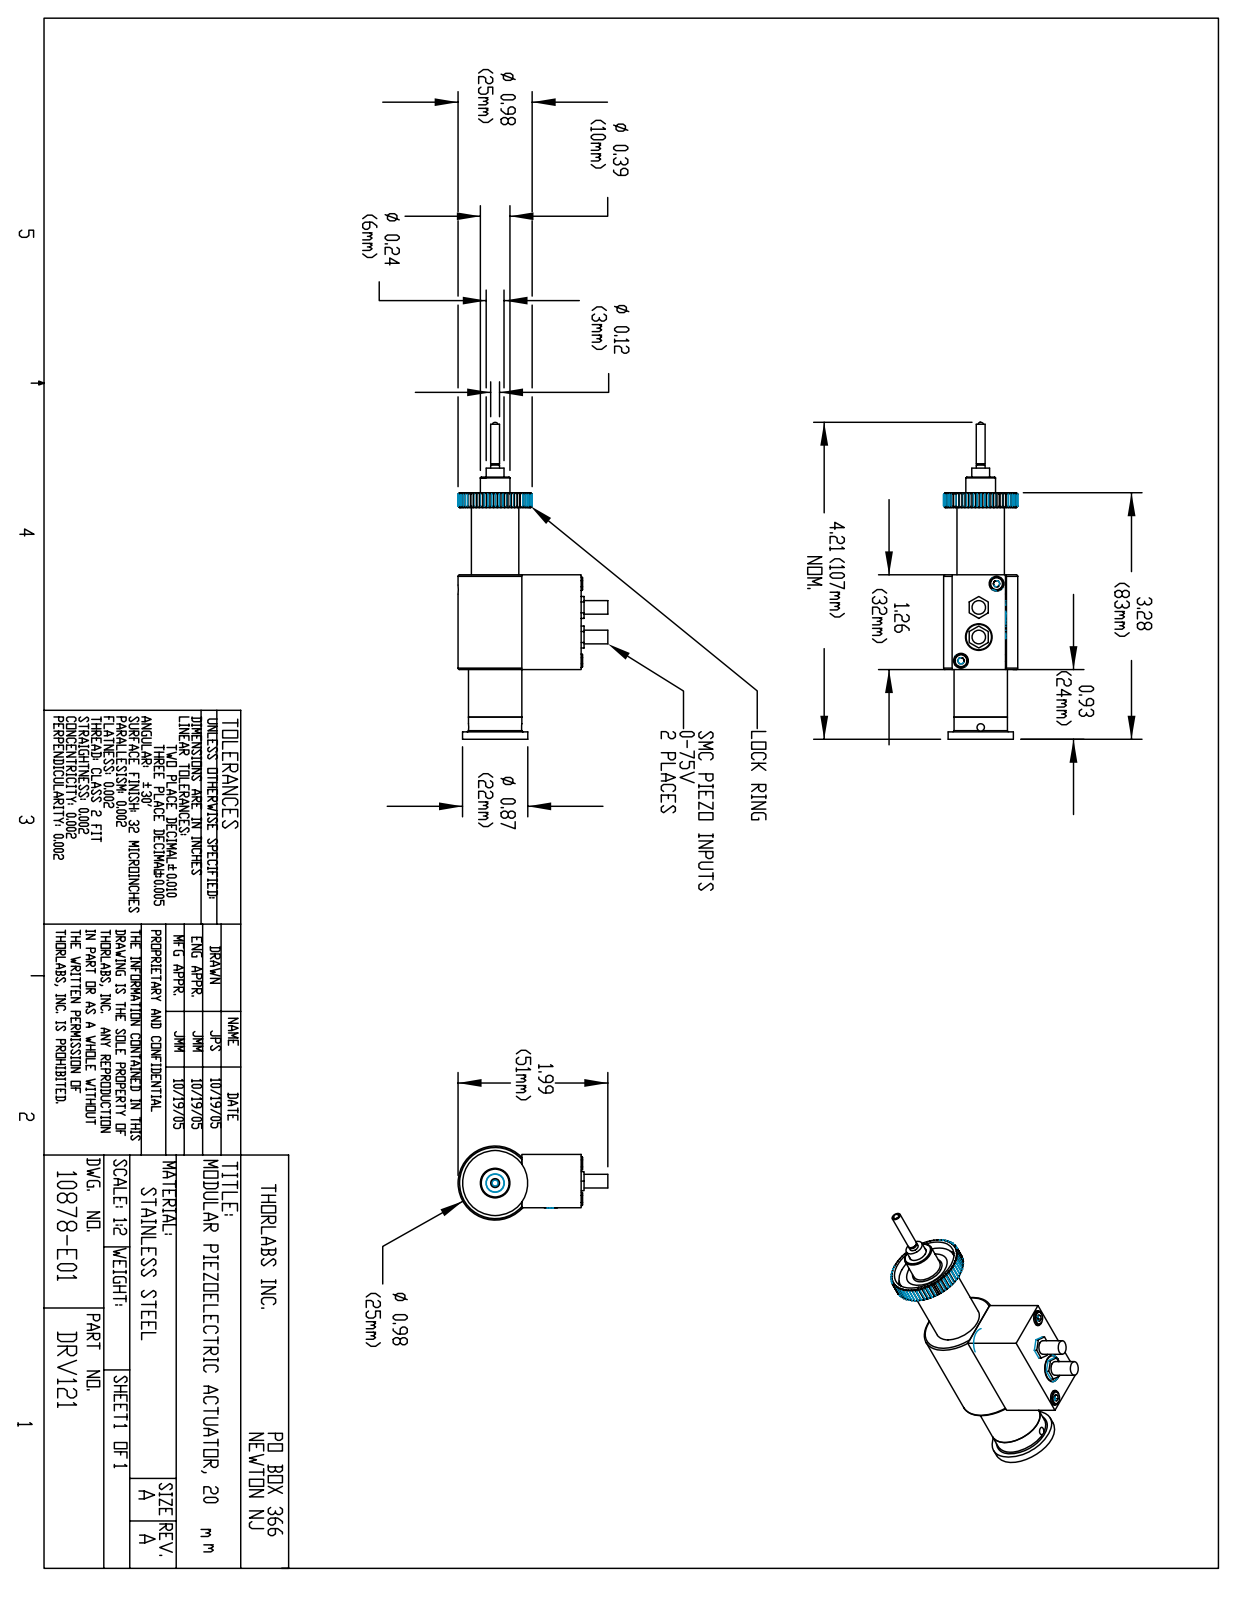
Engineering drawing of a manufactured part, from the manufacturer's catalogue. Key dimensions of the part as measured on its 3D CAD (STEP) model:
Part name (STEP PRODUCT): 10878-E0W
STEP written by: SolidWorks 2007 (AUTOMOTIVE_DESIGN)
Units: inches
Bodies: 0 solids, 483 faces (213 planar, 121 cylindrical, 149 other)
Overall size (bounding box): 4.213 × 1.988 × 0.984
Round holes (diameter × count): ⌀0.098 ×2, ⌀0.197 ×2, ⌀0.079 ×1, ⌀0.244 ×1, ⌀0.354 ×1, ⌀0.394 ×1, ⌀0.724 ×1, ⌀0.866 ×1
Round bosses / shafts (diameter × count): ⌀0.181 ×2, ⌀0.177 ×2, ⌀0.811 ×1, ⌀0.709 ×1, ⌀0.63 ×1, ⌀0.236 ×1, ⌀0.118 ×1, ⌀0.098 ×1
Partial cylindrical surfaces — rounded edges, fillets, slot ends (radius × count): R0.197 ×3, R0.087 ×2, R0.492 ×1
Main face-to-face distances: 0.709, 1.26, 0.059, 0.787, 2.185, 0.945, 2.205, 3.13, 0.925, 0.295
Hole centre spacings: 0.225, 0.394, 0.63, 0.747, 0.924, 0.98, 1.128, 1.201
